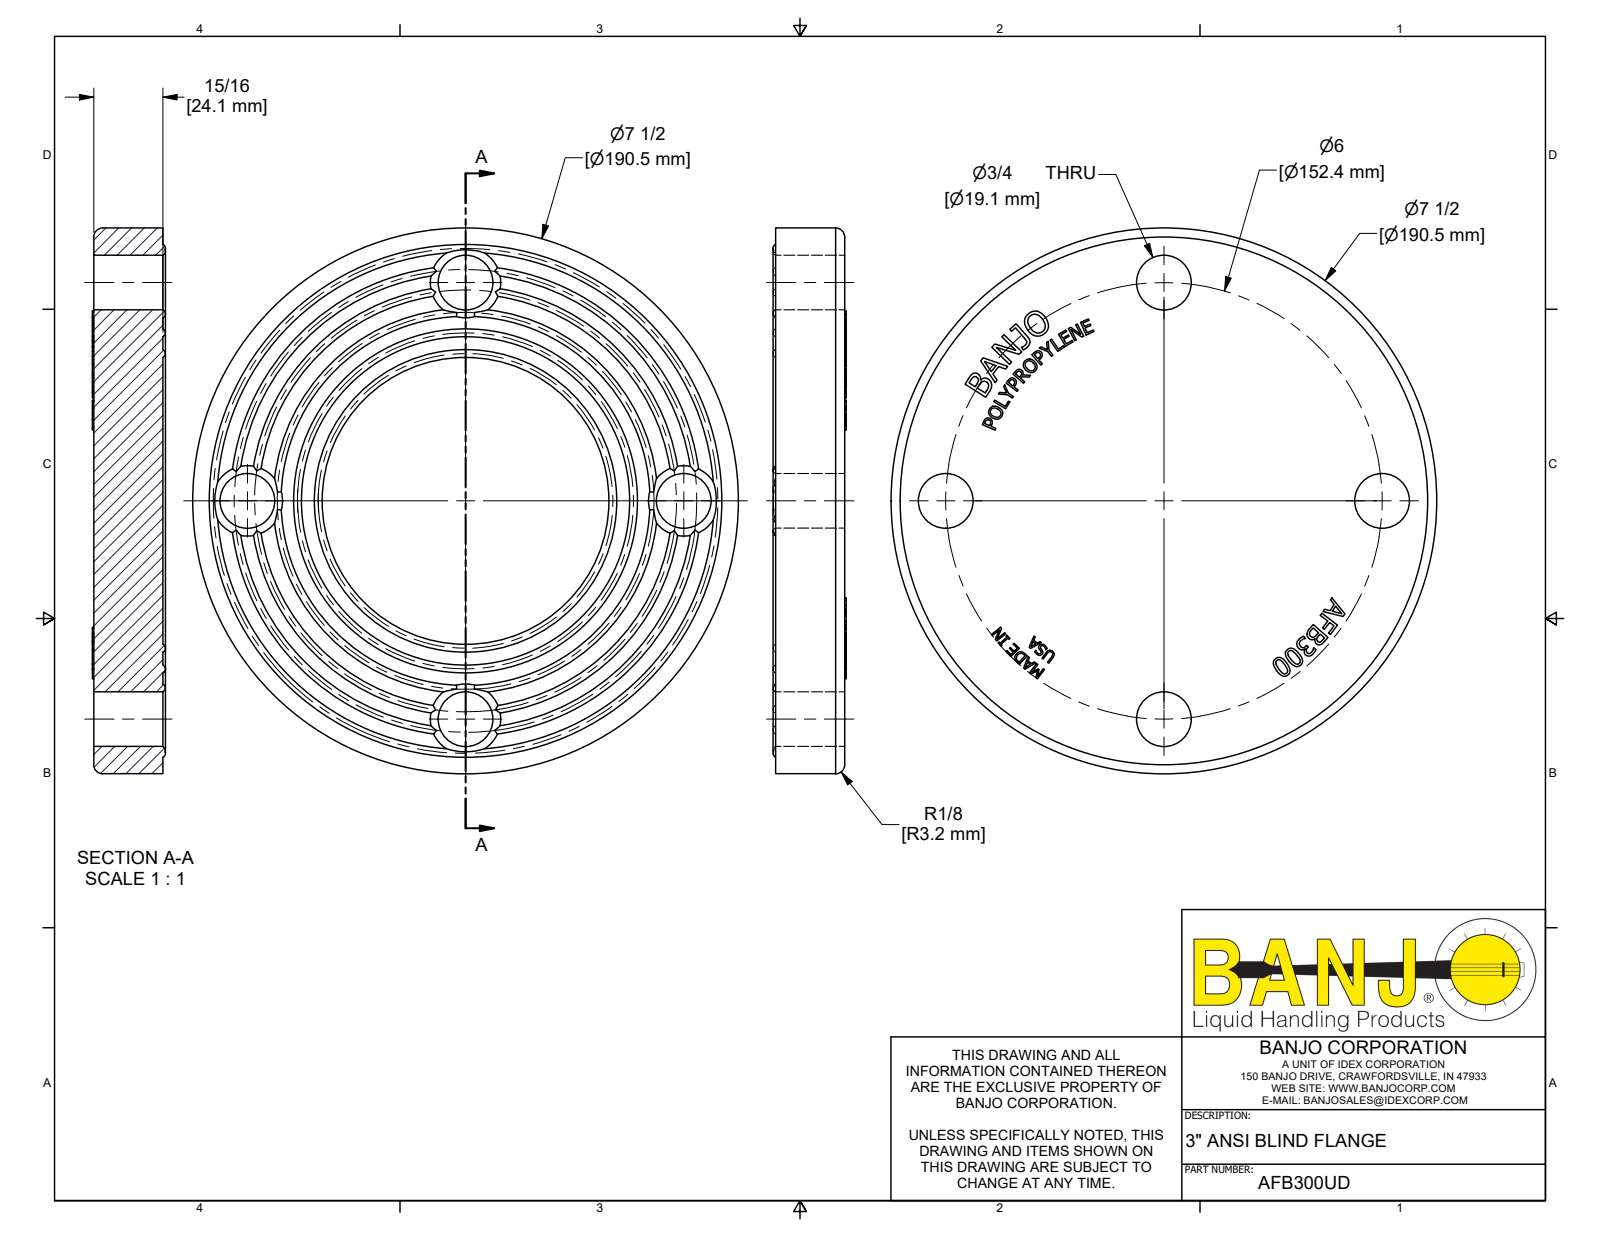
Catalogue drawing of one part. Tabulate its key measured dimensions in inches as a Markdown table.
| quantity | value |
| --- | --- |
| part name | AFB300; AFB300UD |
| STEP written by | Autodesk Inventor 2022 (AUTOMOTIVE_DESIGN) |
| units | inches |
| bodies | 1 solid, 535 faces (329 planar, 5 cylindrical, 201 other) |
| overall size | 7.5 × 7.5 × 1.005 |
| volume | 40.51 in³ |
| surface area | 118.4 in² |
| round holes (diameter × count) | 0.75 × 4 |
| round bosses / shafts (diameter × count) | 7.5 × 1 |
| main face-to-face distances | 0.95, 0.02, 0.97, 0.025, 0.022, 0.021, 0.042, 0.2, 0.045, 0.036 |
| hole center spacings | 4.243, 6 |
